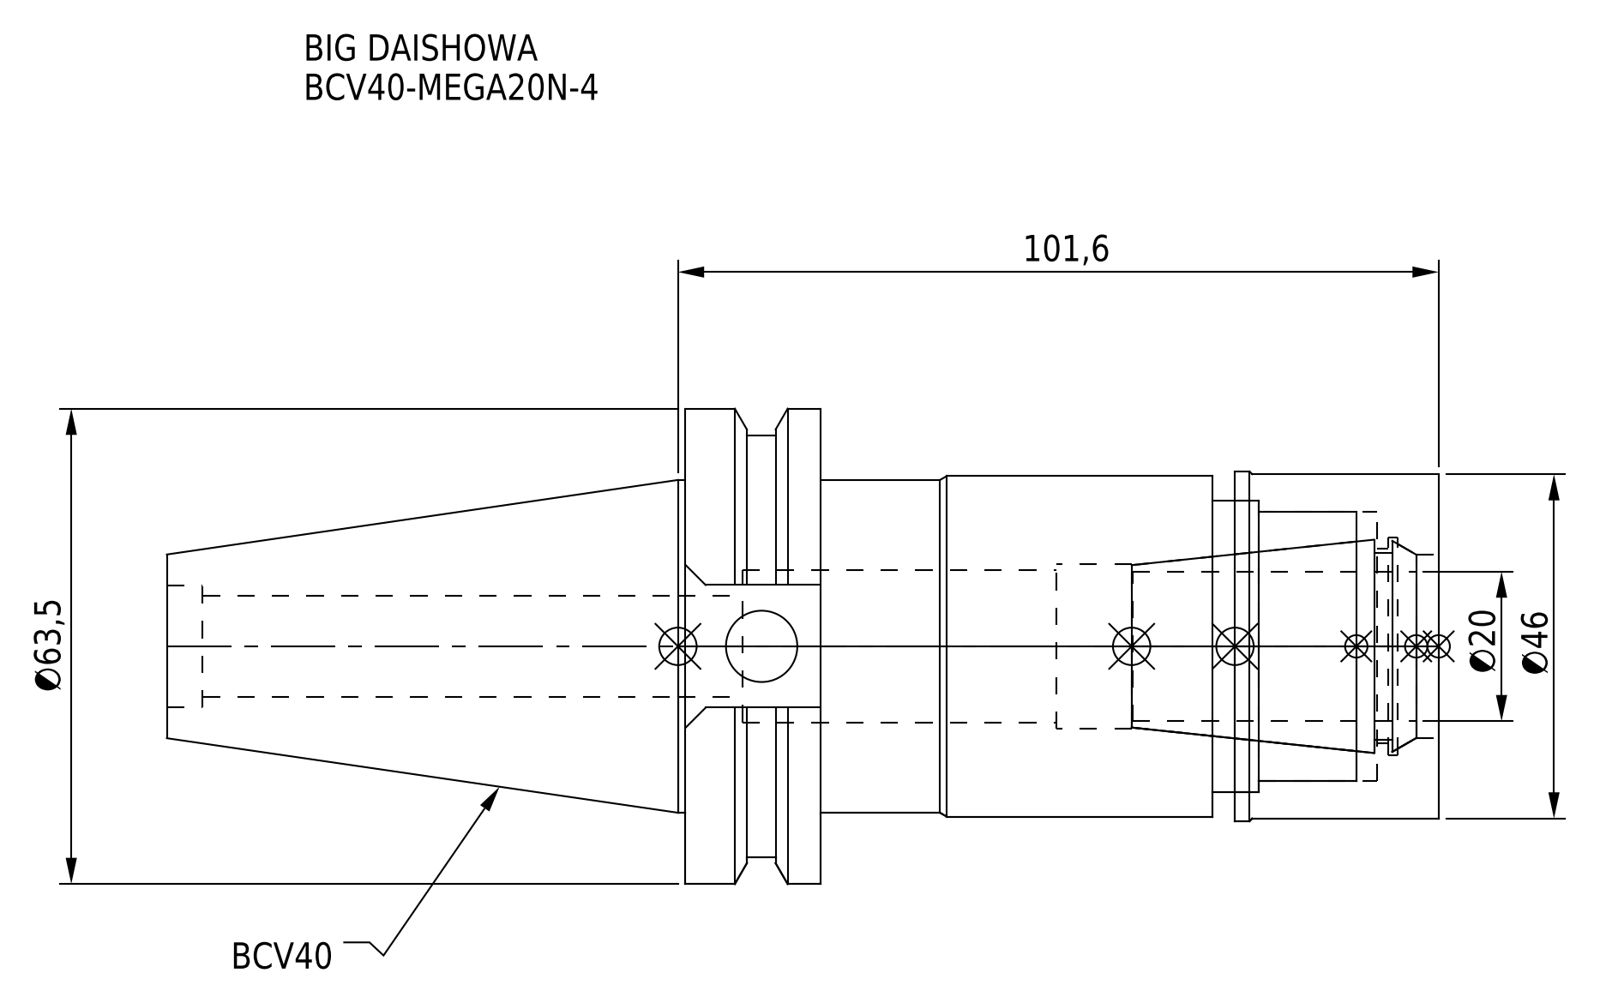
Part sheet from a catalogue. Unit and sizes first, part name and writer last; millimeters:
Units: millimetres
Overall size (bounding box): 169.85 × 63.5 × 61.35
Round holes (diameter × count): ⌀9.53 ×1, ⌀13.6 ×1, ⌀16.32 ×1, ⌀20.3 ×1, ⌀22 ×1, ⌀24.5 ×1, ⌀26 ×1, ⌀29 ×1, ⌀36 ×1, ⌀39 ×1
Round bosses / shafts (diameter × count): ⌀63.5 ×1, ⌀56.36 ×1, ⌀46.7 ×1, ⌀46 ×1, ⌀45.5 ×1, ⌀44.45 ×1
Main face-to-face distances: 18.05, 82.55, 100.6, 27.2, 55.35, 73.4, 8.2, 19, 74.35, 92.4
Volume: 198 935 mm³ · Surface area: 44 667 mm²
Bodies: 2 solids, 87 faces (31 planar, 42 cylindrical, 14 other)
Part name (STEP PRODUCT): BCV40-MEGA20N-4; MGN20_1.stp; BCV40-MEGA20N-4-200-FreeParts; BCV40MN20040-200_ASM.stp (+3 more)
STEP written by: SolidWorks 2019 (CONFIG_CONTROL_DESIGN)
